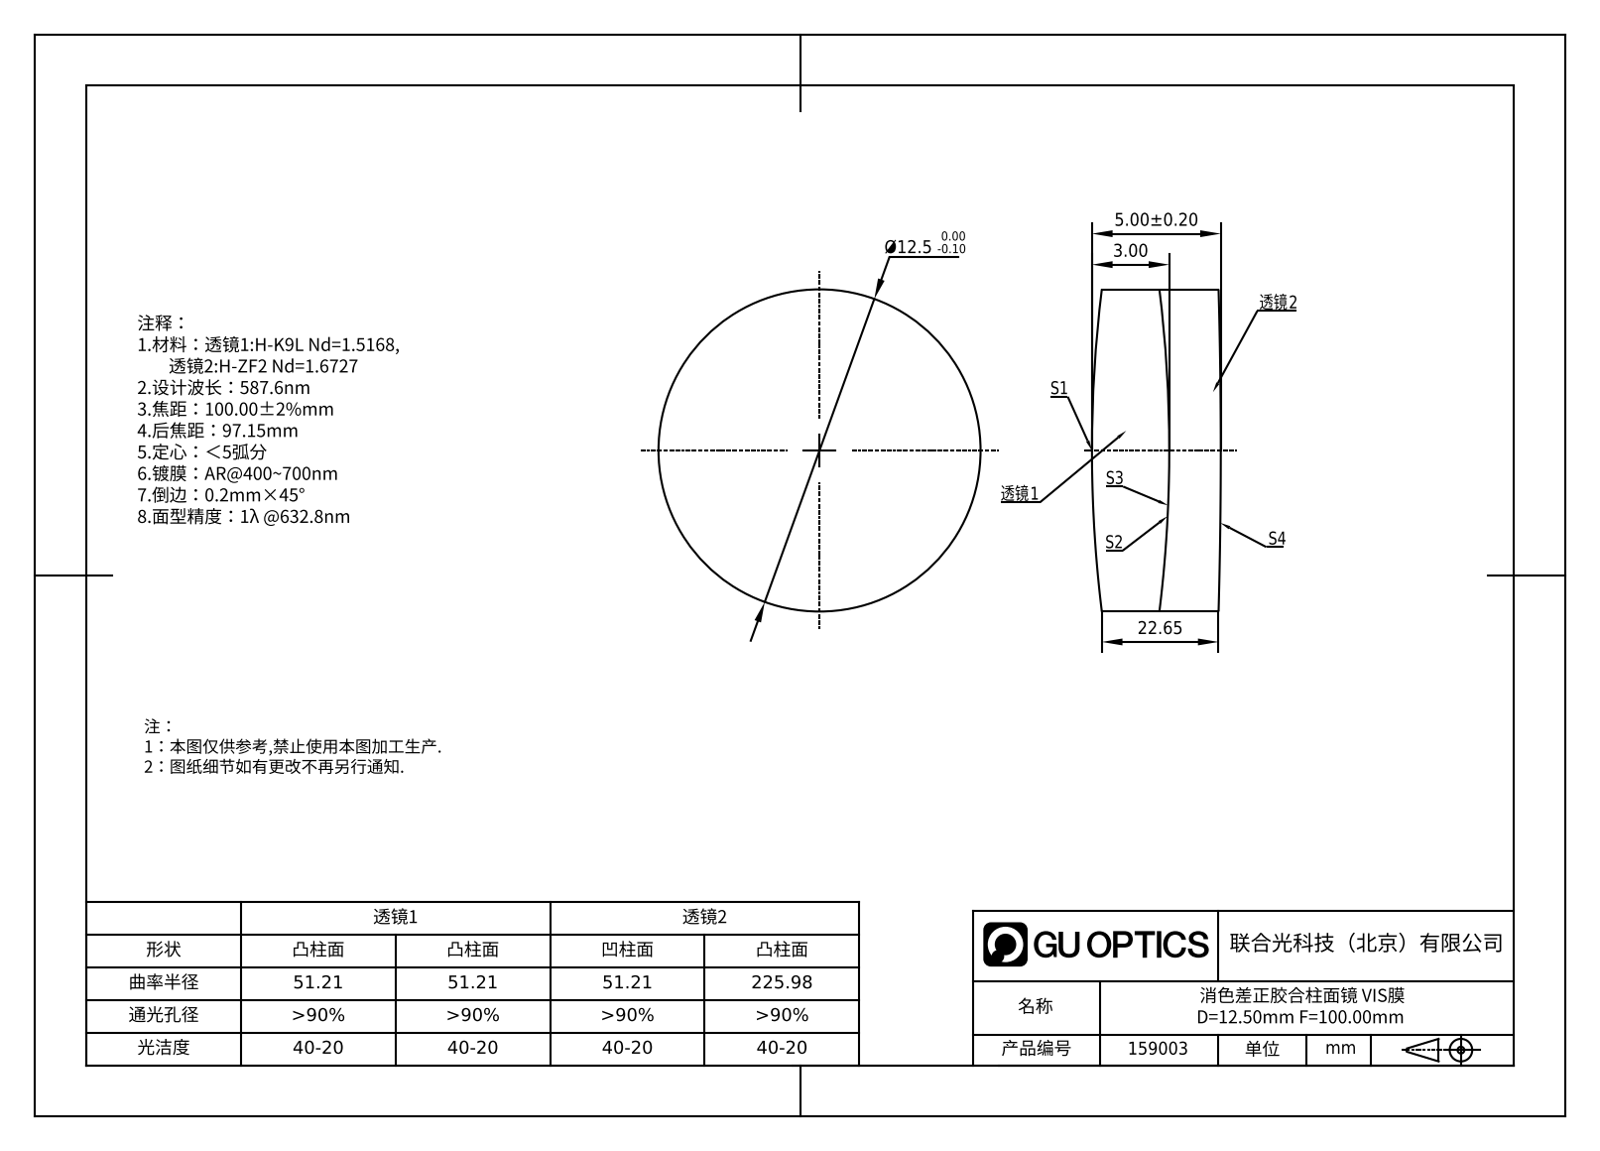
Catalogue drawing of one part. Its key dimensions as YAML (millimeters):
part_name: "159003"
step_written_by: "SolidWorks 2020 (CONFIG_CONTROL_DESIGN)"
units: millimeters
bodies: {solids: 1, faces: 5, planar: 0, cylindrical: 5, other: 0}
overall_size: [12.5, 12.5, 5]
volume: 599
surface_area: 433
round_bosses_or_shafts:
  - {diameter: 12.5, count: 1}
partial_cylinders:
  - {radius: 51.21, count: 1}
  - {radius: 225.98, count: 1}
